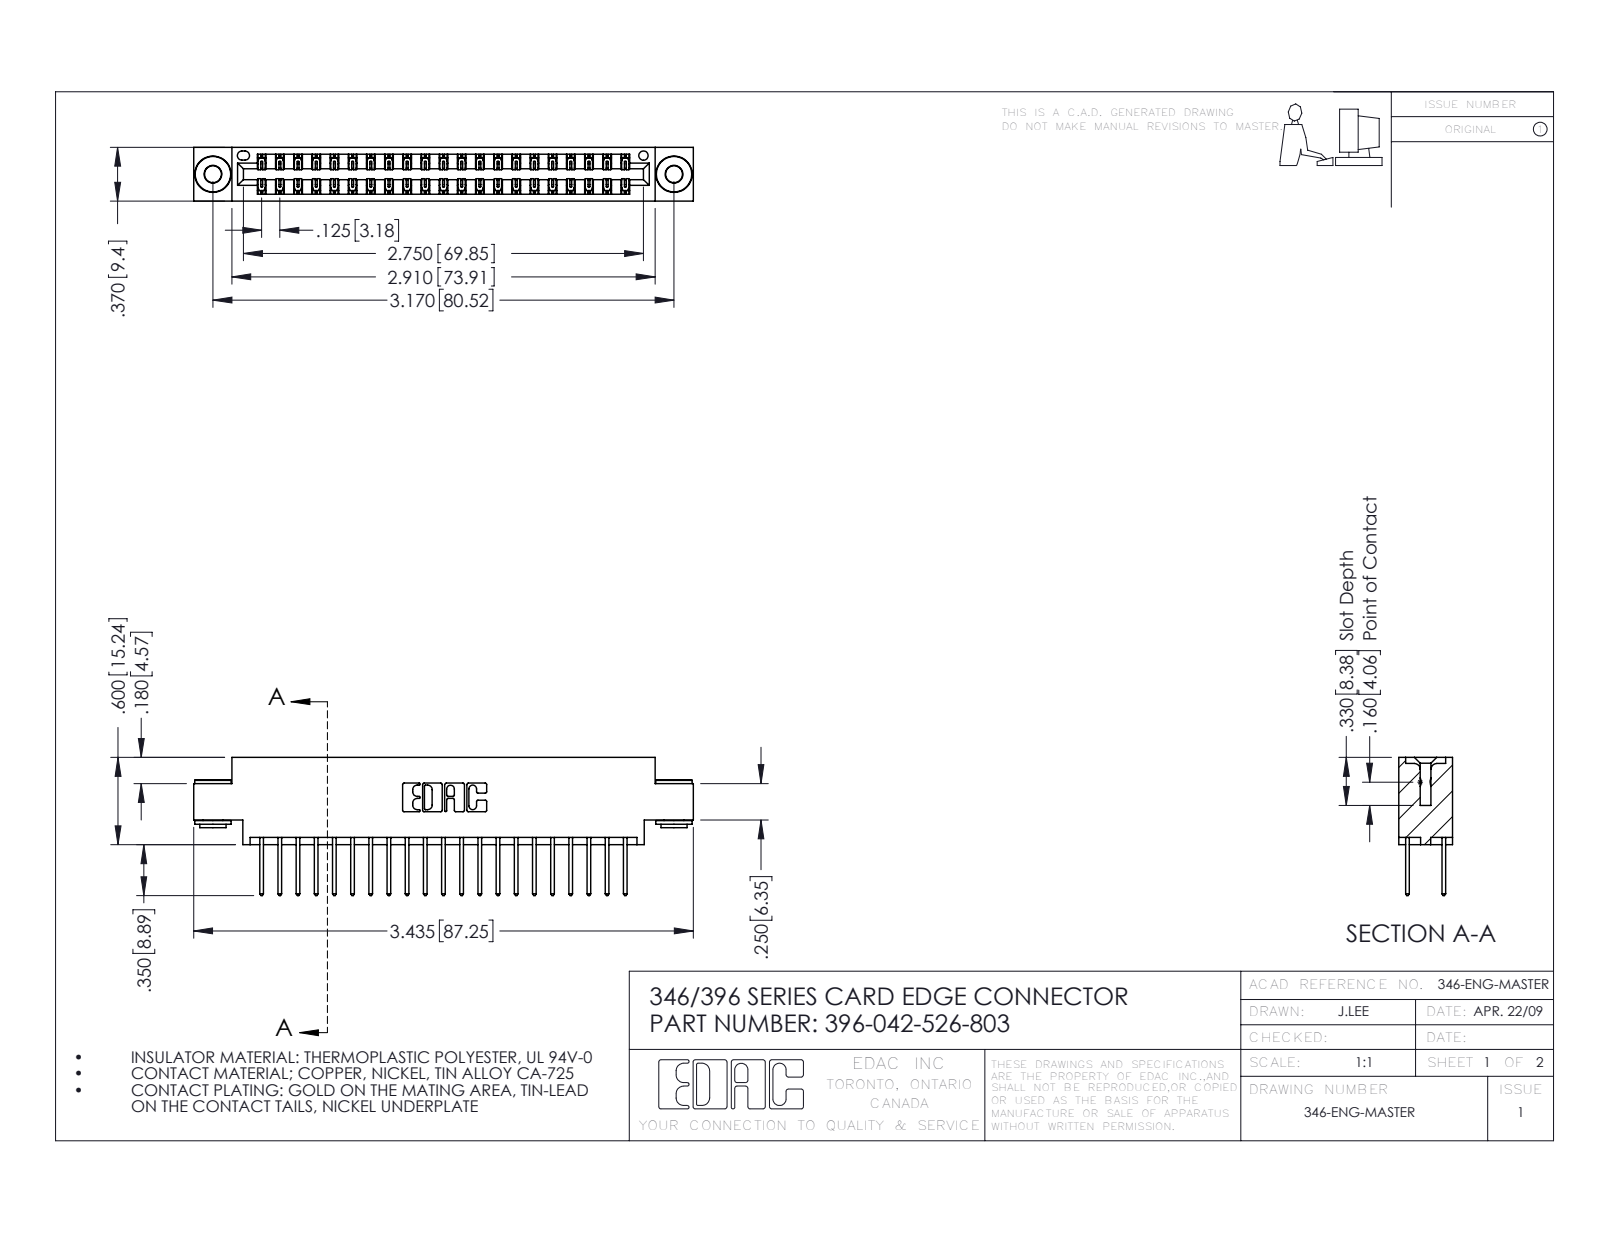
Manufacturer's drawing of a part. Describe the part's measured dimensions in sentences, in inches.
The part is named "345-250-002_345-250-002-102; 346 Part_0.170 Offset - 0.156 Dia-TH; 345-292-001_345-293-126; 396-042-526-803". Its 3-D file was written by "SolidWorks 2016 (CONFIG_CONTROL_DESIGN)". It is 45 solids with 2348 faces: 1560 planar, 780 cylindrical and 8 other. Overall it measures 3.435 by 0.95 by 0.37 inches. Its volume is 0.505 cubic inches and its surface area 18.21 square inches. Round holes: 2 of diameter 0.116, 2 of diameter 0.156, 1 of diameter 0.064. Round bosses or shafts: 2 of diameter 0.25, 2 of diameter 0.18, 2 of diameter 0.136. Partial cylindrical surfaces (rounded edges, fillets, slot ends): 63 of radius 0.006, 42 of radius 0.01, 22 of radius 0.01, 6 of radius 0.007, 6 of radius 0.031, 3 of radius 0.026, 2 of radius 0.014, 2 of radius 0.022. The main face-to-face distances are 0.048, 0.322, 0.25, 0.37, 0.025, 0.072, 0.298, 0.275, 0.148, 0.222. The hole center spacings are 0.246, 2.963, 3.17.
